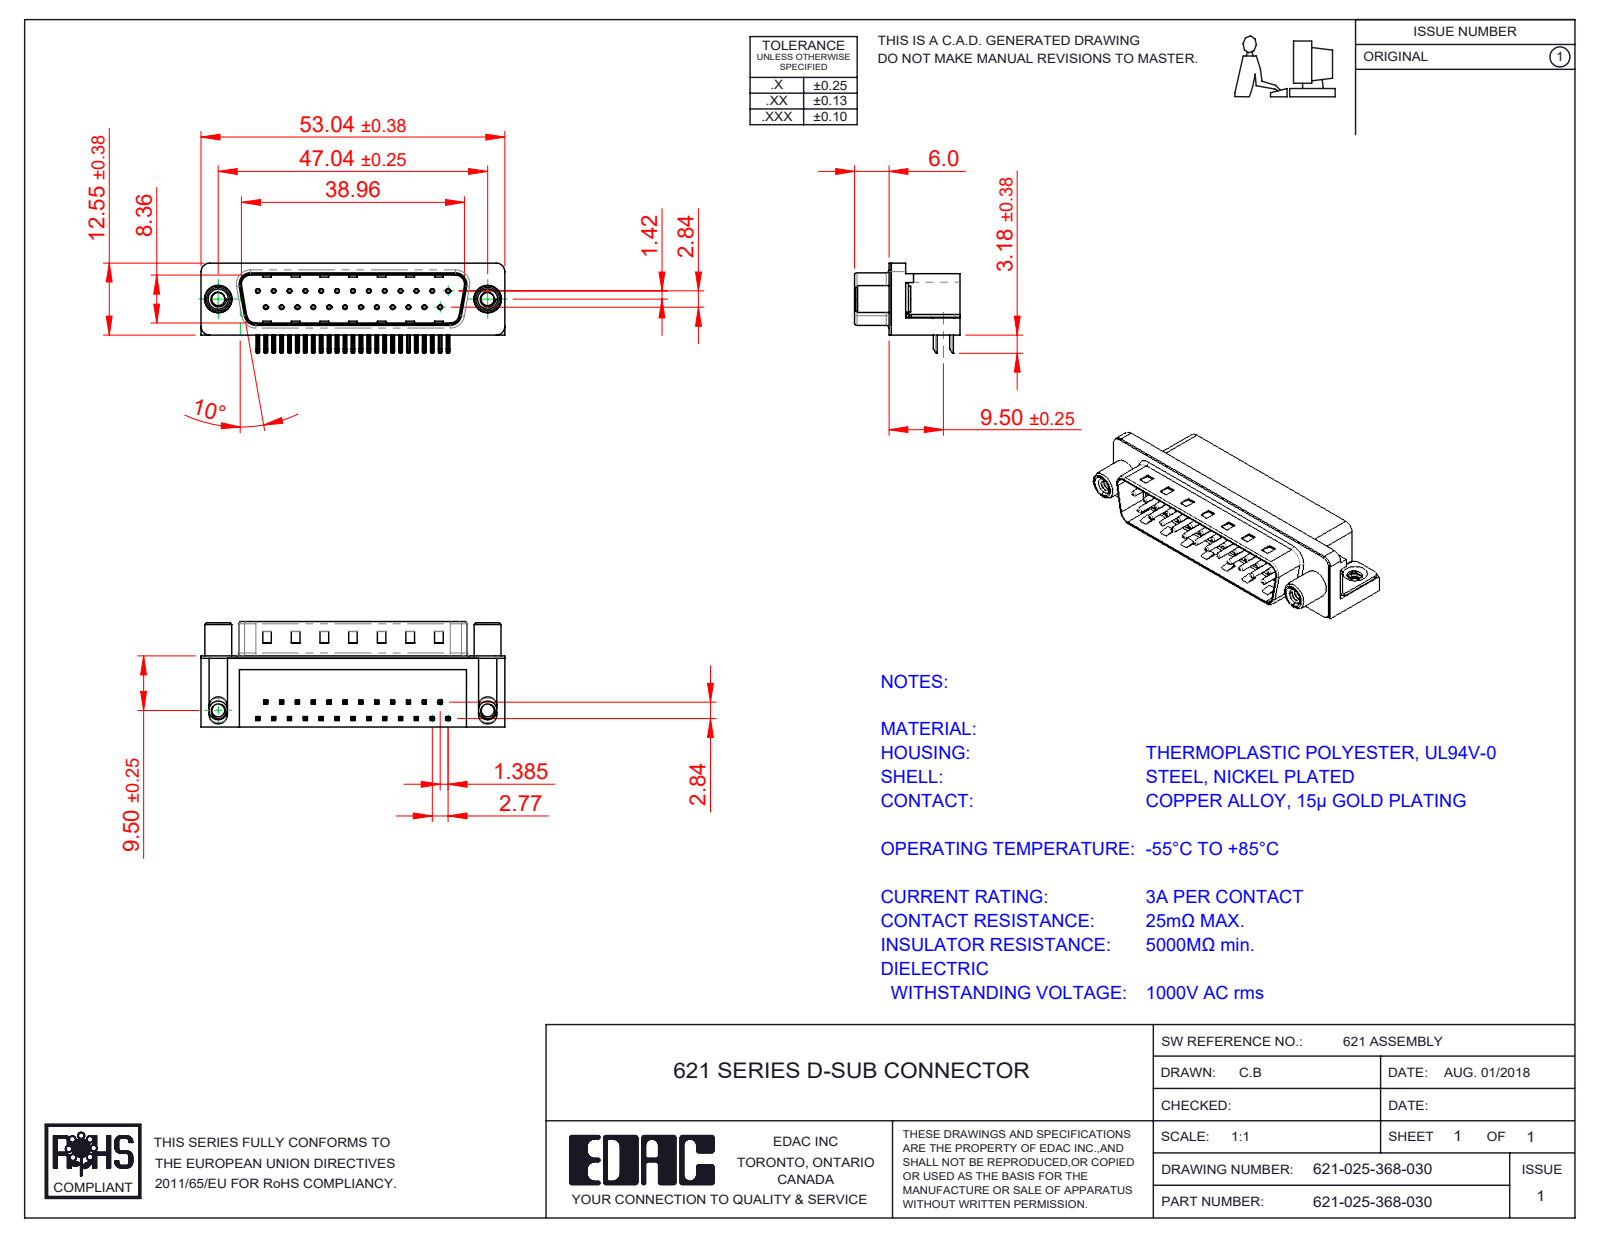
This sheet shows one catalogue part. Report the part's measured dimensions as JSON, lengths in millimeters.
{"part_name": "621 2 Prong Board Lock; 621 Contact Top; 621-025-368-030; 621 Round Threaded Standoff (+3 more)", "step_written_by": "SolidWorks 2016 (CONFIG_CONTROL_DESIGN)", "units": "millimeters", "bodies": {"solids": 31, "faces": 2297, "planar": 1429, "cylindrical": 675, "other": 193}, "overall_size": [53.04, 18.4, 16.25], "volume_mm3": 6437, "surface_area_mm2": 7888, "round_holes": [[0.35, 25], [0.8, 25], [2.3, 2], [3.1, 2], [4, 2], [4.8, 2], [5, 2]], "round_bosses_or_shafts": [[0.75, 25], [4.9, 2], [4.7, 2], [4.5, 2], [3.85, 2]], "partial_cylinders_radius": [[0.25, 100], [0.12, 50], [1, 16], [0.5, 14], [1.6, 8], [1.5, 7], [0.32, 4], [0.9, 4]], "face_to_face_distances": [0.4, 12, 10.35, 2.1, 8.76, 10.46, 1.7, 10.86, 12.4, 9], "hole_center_spacings": [3.16, 2.77, 5.54, 8.31, 11.08, 13.85, 16.62, 5.03]}
